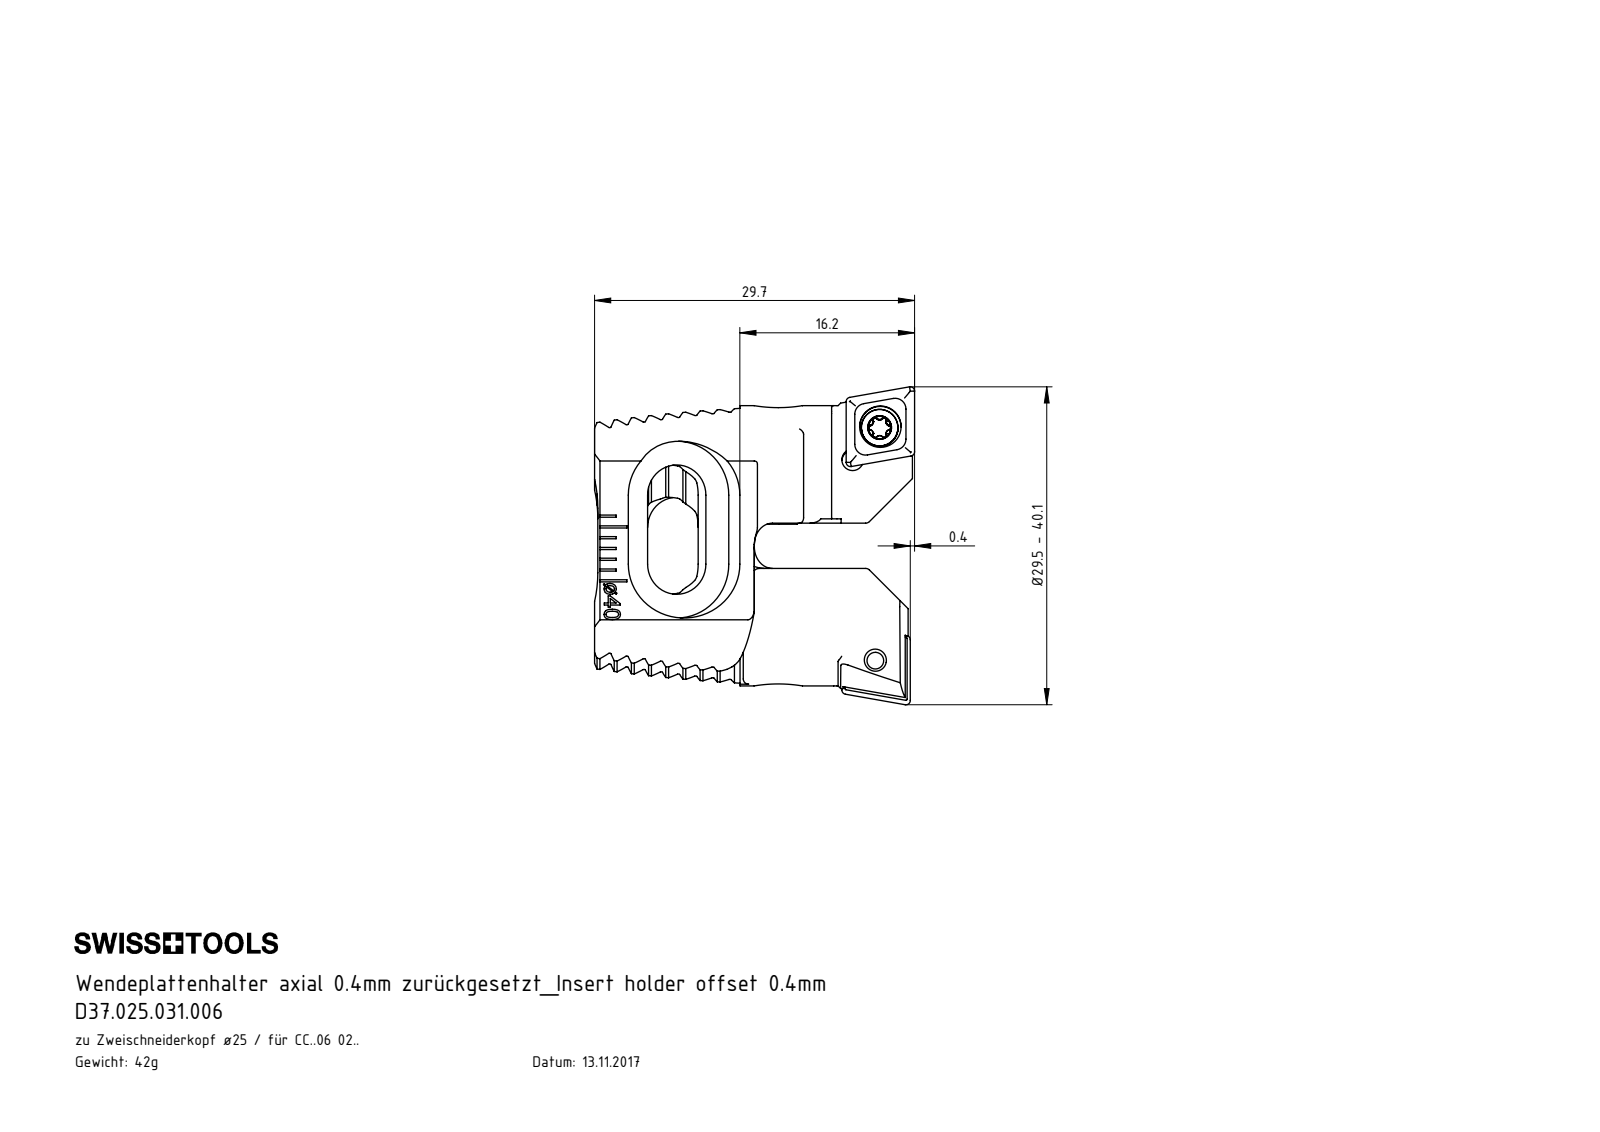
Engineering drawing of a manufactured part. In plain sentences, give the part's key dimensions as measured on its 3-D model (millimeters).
The part is named "D37.025.031.006; WCA-ER2.001.006_B; CCMT060204; Z25-ER3.001.010_A (+3 more)". Its 3-D file was written by "SolidWorks 2017 (CONFIG_CONTROL_DESIGN)". It is 9 solids with 680 faces: 313 planar, 161 cylindrical and 206 other. Overall it measures 29.7 by 29.5 by 20.29 millimeters. Its volume is 5 270 cubic millimeters and its surface area 4 868 square millimeters. Round holes: 4 of diameter 1.6, 2 of diameter 2, 2 of diameter 2.05, 2 of diameter 2.8, 2 of diameter 3.85, 1 of diameter 3.5. Round bosses or shafts: 2 of diameter 3.4, 2 of diameter 2.5, 1 of diameter 4. Partial cylindrical surfaces (rounded edges, fillets, slot ends): 18 of radius 0.5, 16 of radius 0.12, 12 of radius 0.21, 10 of radius 0.36, 4 of radius 2, 4 of radius 2.8, 4 of radius 5, 4 of radius 12. The main face-to-face distances are 1.43, 2.86, 4.29, 5.72, 7.15, 3.9, 8.58, 4.6, 10, 0.4. The hole center spacings are 3.91, 4.01, 7, 21.97, 2.49, 2.51, 5, 7.43.
